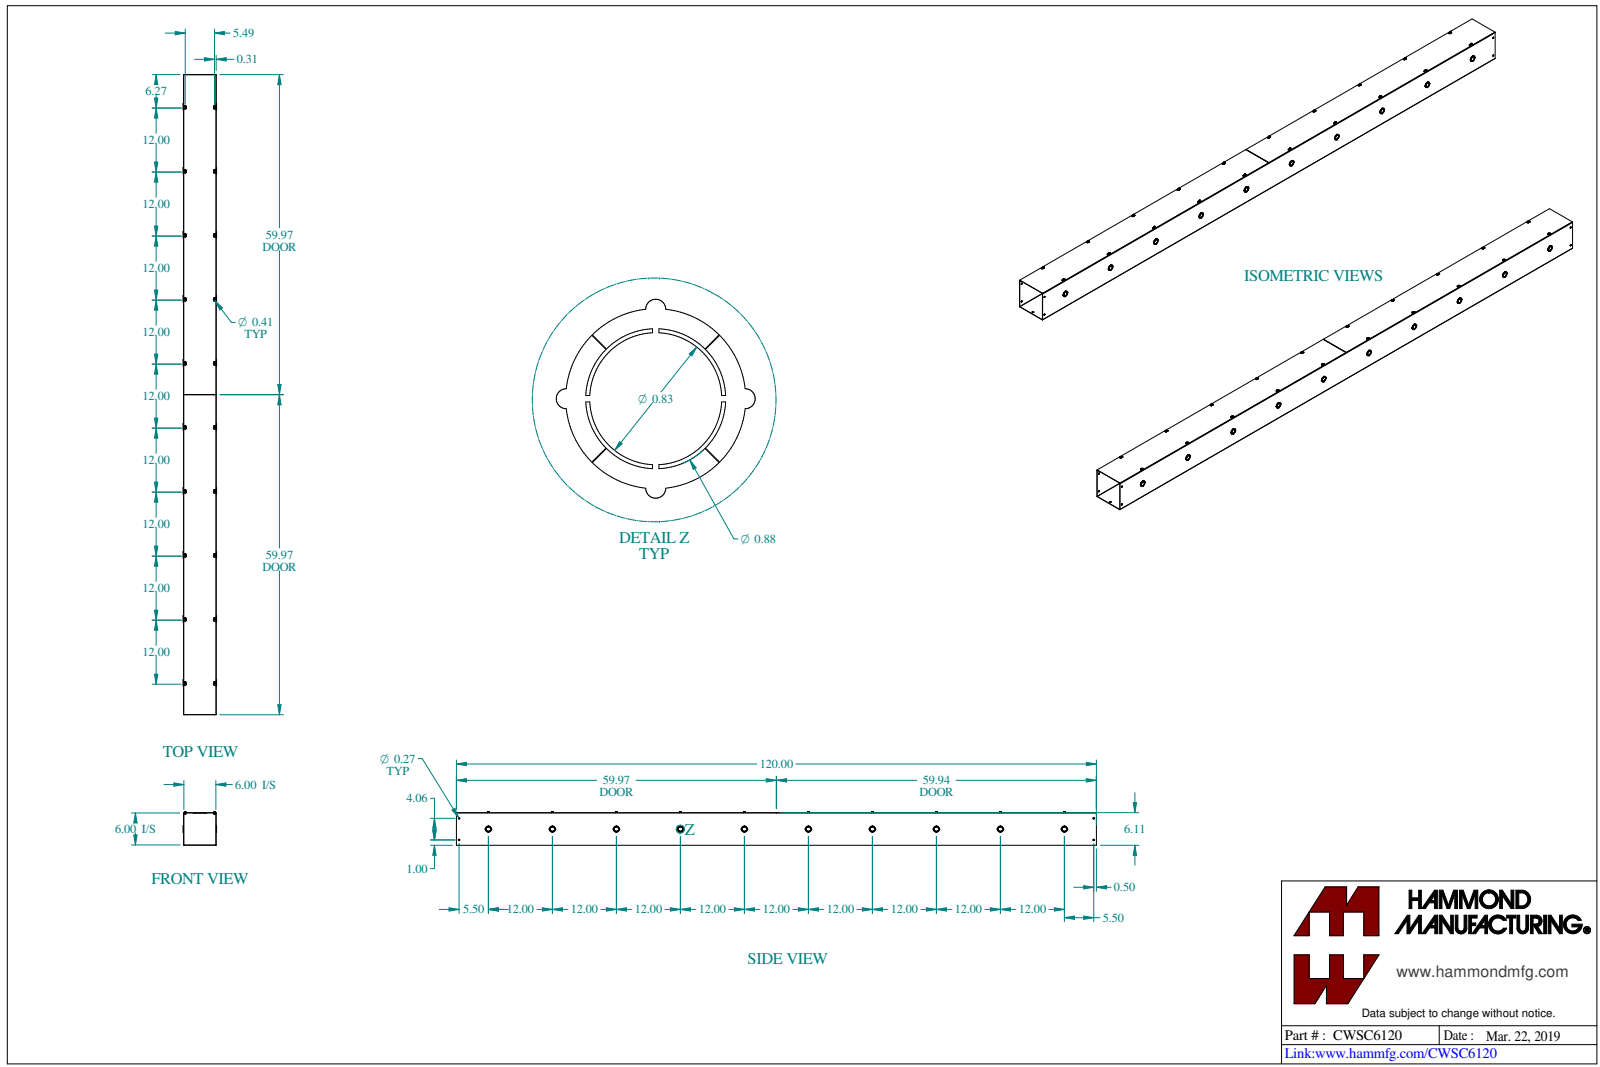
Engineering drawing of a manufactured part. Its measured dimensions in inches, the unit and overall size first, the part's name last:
Units: inches
Overall size (bounding box): 120 × 6.289 × 6.258
Round holes (diameter × count): ⌀0.177 ×20, ⌀0.875 ×10, ⌀0.266 ×4, ⌀0.313 ×2
Round bosses / shafts (diameter × count): ⌀0.375 ×20, ⌀0.19 ×20, ⌀1.125 ×10, ⌀0.825 ×10
Partial cylindrical surfaces — rounded edges, fillets, slot ends (radius × count): R0.063 ×40, R0.125 ×20, R0.203 ×20, R0.062 ×10, R0.029 ×4, R0.086 ×4
Main face-to-face distances: 0.057, 6.057, 6, 6.114, 5.943, 0.114, 0.072, 0.129, 6.129, 6.186
Hole centre spacings: 12, 24, 36, 13.196, 48, 24.62, 60, 36.416
Volume: 172.2 in³ · Surface area: 6 036 in²
Bodies: 23 solids, 1522 faces (674 planar, 728 cylindrical, 120 other)
Part name (STEP PRODUCT): CWSC6120
STEP written by: SolidWorks 2023 (CONFIG_CONTROL_DESIGN)
